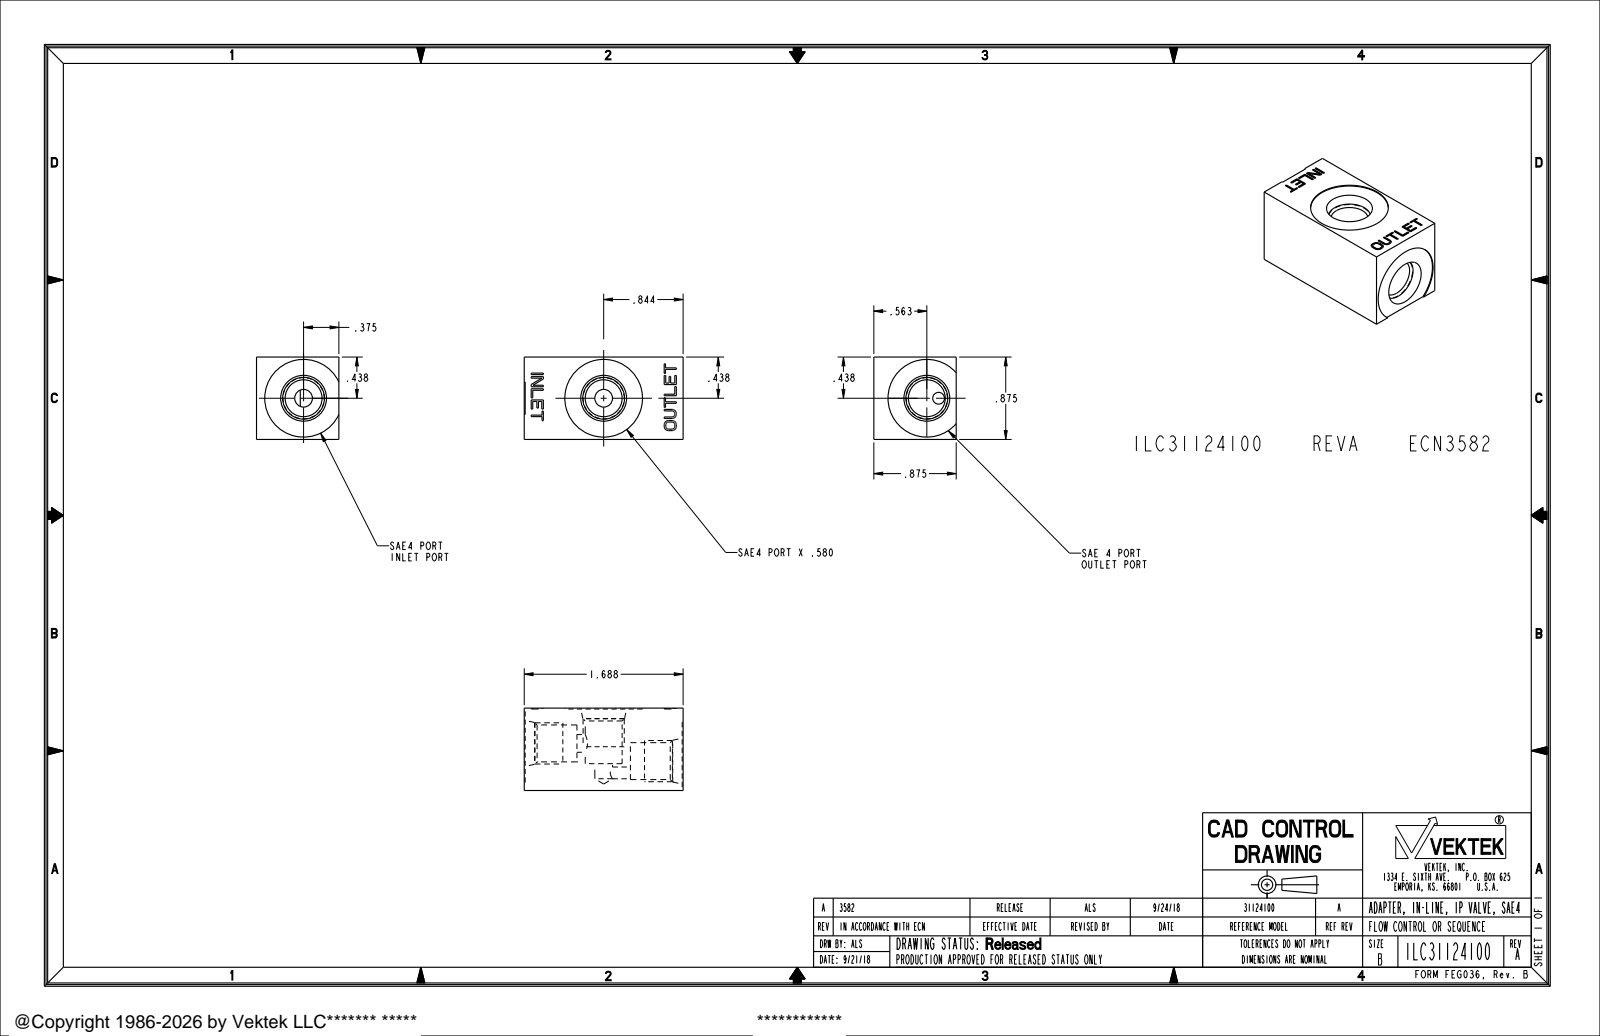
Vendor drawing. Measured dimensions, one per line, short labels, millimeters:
name: ILC31124100
written by: PRO/ENGINEER BY PARAMETRIC TECHNOLOGY CORPORATION, 2013320 (AUTOMOTIVE_DESIGN)
unit: mm
bodies: 1 solid, 207 faces (171 planar, 22 cylindrical, 14 other)
size: 42.9 × 22.2 × 22.2
volume: 17 160 mm³; area: 7 116 mm²
holes: 3× ⌀10, 2× ⌀4.8, 2× ⌀21, 1× ⌀3.2
bosses: 3× ⌀11.1
rounds: 1× R10.5
face distances: 22.2, 42.6, 22, 42.4, 42.9, 14.2, 28.7, 14, 28.4, 7.2
hole spacings: 3.2, 4.8, 8
